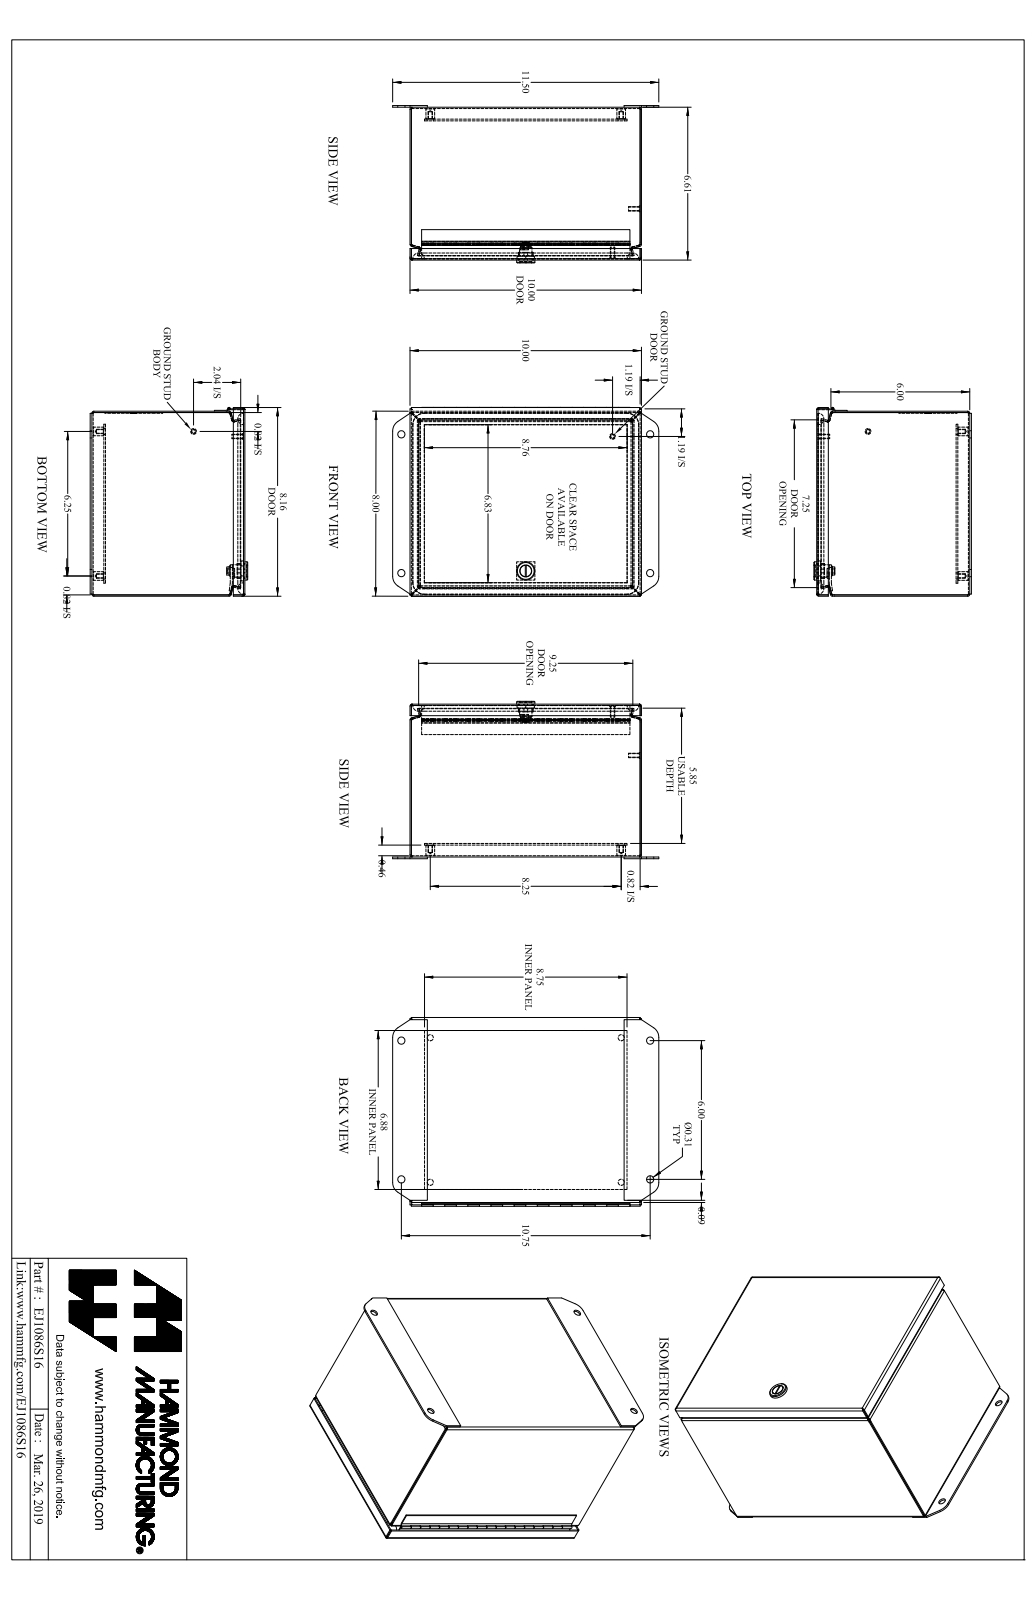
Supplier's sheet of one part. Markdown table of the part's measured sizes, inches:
| quantity | value |
| --- | --- |
| part name | EJ1086S16_Default |
| STEP written by | SolidWorks 2019 (CONFIG_CONTROL_DESIGN) |
| units | inches |
| bodies | 16 solids, 596 faces (310 planar, 206 cylindrical, 80 other) |
| overall size | 11.5 × 8.165 × 6.805 |
| volume | 33.43 in³ |
| surface area | 1 109 in² |
| round holes (diameter × count) | 0.156 × 4, 0.265 × 4, 0.313 × 4, 0.05 × 1, 0.516 × 1 |
| round bosses / shafts (diameter × count) | 0.375 × 4, 0.25 × 2, 0.19 × 2, 0.788 × 1, 0.535 × 1, 0.496 × 1, 0.435 × 1, 0.1 × 1 |
| partial cylindrical surfaces (radius × count) | 0.029 × 16, 0.086 × 16, 0.281 × 12, 0.25 × 4, 0.499 × 4, 0.5 × 4, 0.06 × 2, 0.03 × 1 |
| main face-to-face distances | 0.057, 6.554, 7.943, 9.943, 0.072, 0.589, 6.611, 6.497, 6.094, 6.037 |
| hole center spacings | 1.257, 9.501, 4.131, 5.376, 6, 6.25, 6.251, 6.252 |
